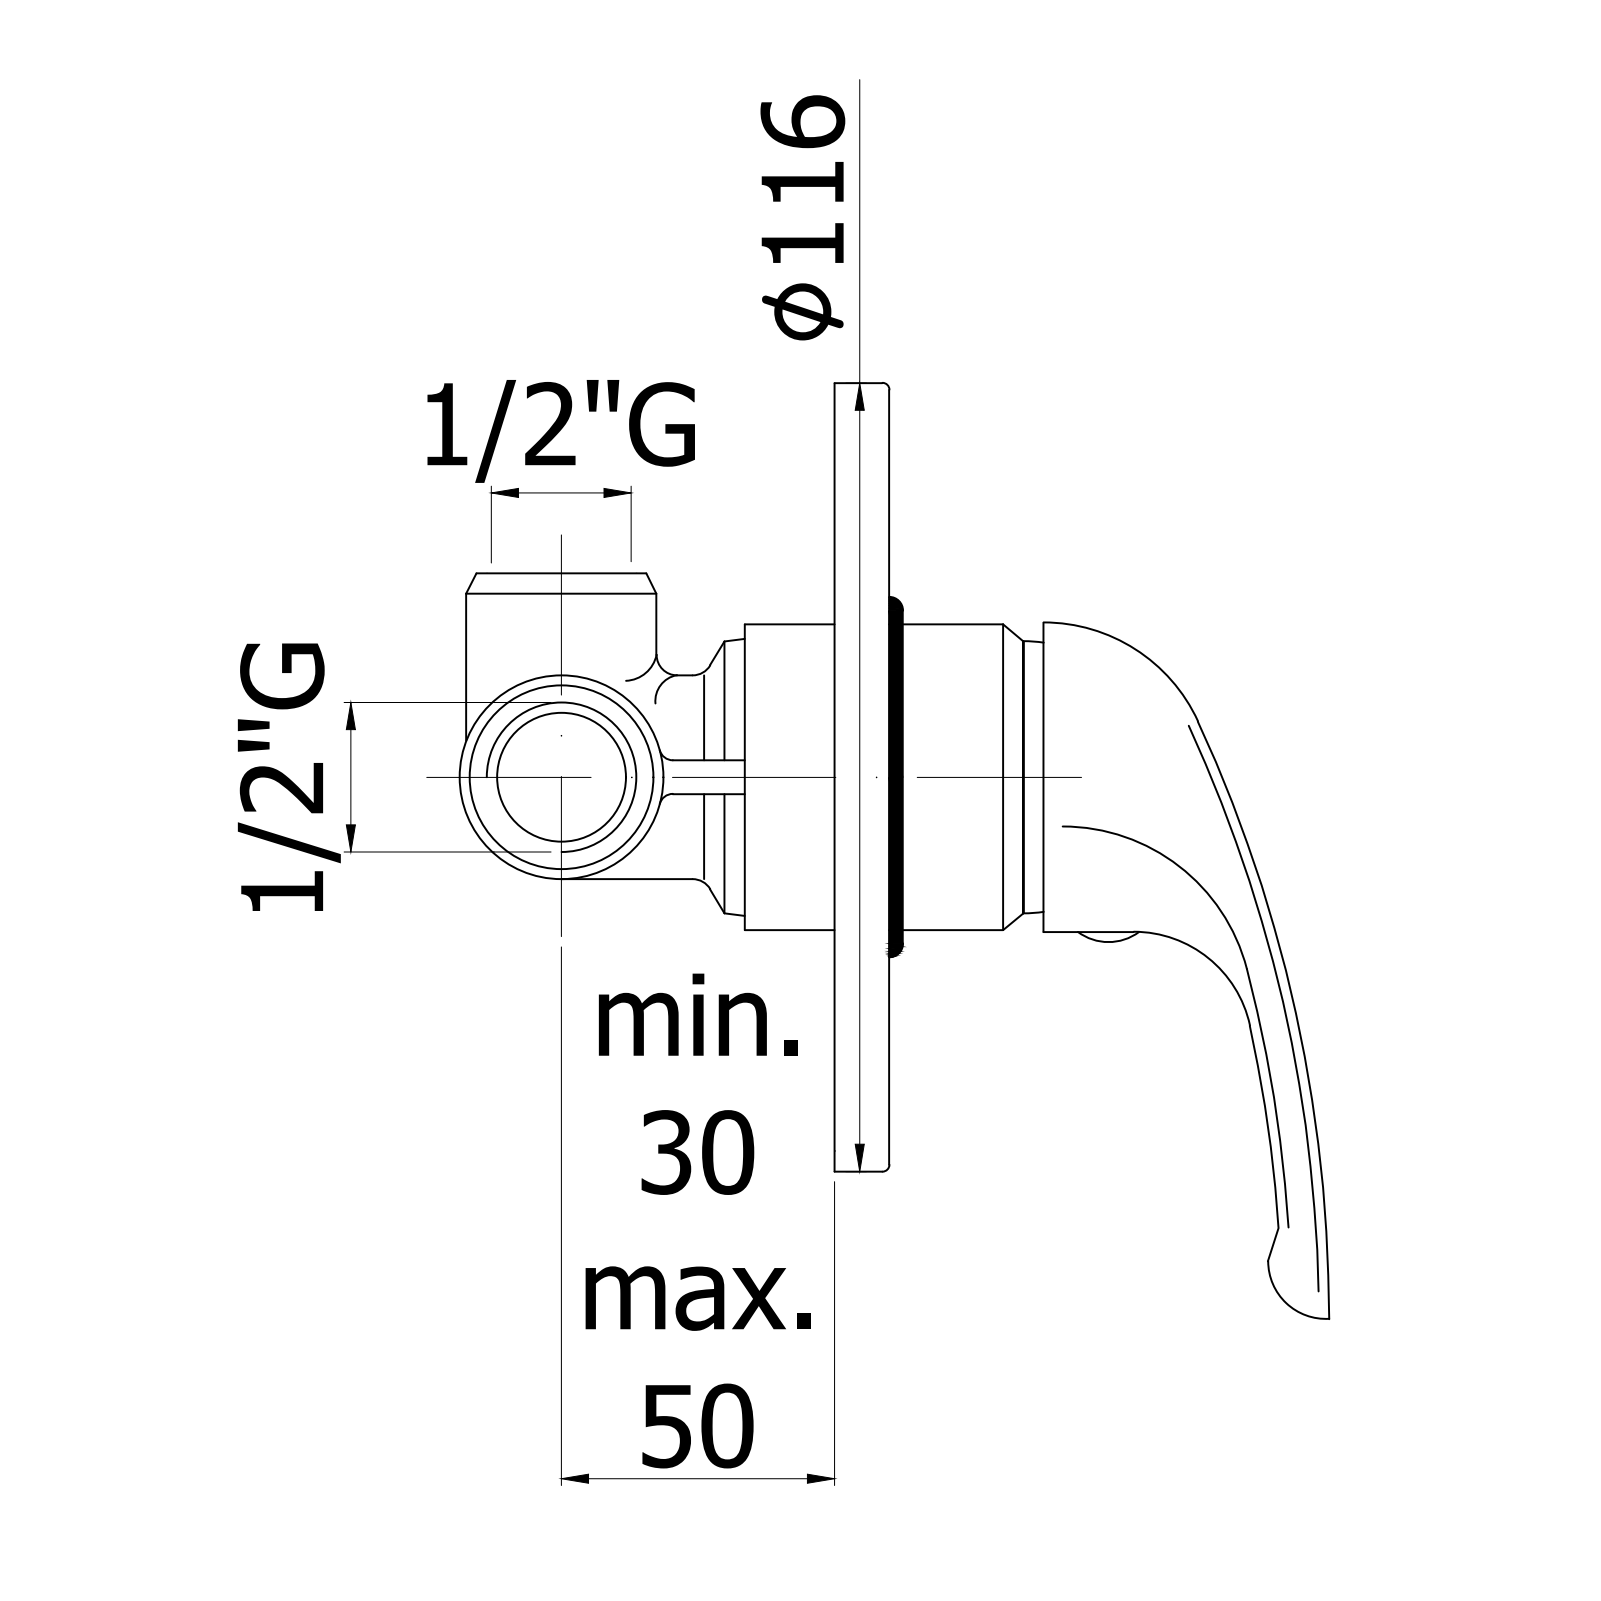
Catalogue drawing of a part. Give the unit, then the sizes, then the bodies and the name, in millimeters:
Units: millimetres
Overall size (bounding box): 135.25 × 116 × 69.1
Round holes (diameter × count): ⌀4 ×2, ⌀3.3 ×1, ⌀4.5 ×1, ⌀5 ×1, ⌀6 ×1, ⌀19.5 ×1, ⌀19.9 ×1, ⌀26.8 ×1, ⌀29 ×1, ⌀31 ×1, ⌀32.4 ×1, ⌀36 ×1
Round bosses / shafts (diameter × count): ⌀116 ×1, ⌀53 ×1, ⌀44.8 ×1, ⌀35 ×1, ⌀23.5 ×1, ⌀23.4 ×1, ⌀21.8 ×1, ⌀8 ×1
Partial cylindrical surfaces — rounded edges, fillets, slot ends (radius × count): R0.15 ×11, R1 ×10, R0.3 ×4, R0.5 ×3, R7 ×1, R9.3 ×1, R10.85 ×1, R11.25 ×1
Main face-to-face distances: 2.5, 11.5, 4, 0.5, 1.5, 4.5, 9, 10, 5.5, 12
Hole centre spacings: 9.3
Volume: 49 937 mm³ · Surface area: 60 203 mm²
Bodies: 2 solids, 846 faces (527 planar, 180 cylindrical, 139 other)
Part name (STEP PRODUCT): APM3010CR
STEP written by: CREO PARAMETRIC BY PTC INC, 2020044 (CONFIG_CONTROL_DESIGN)
